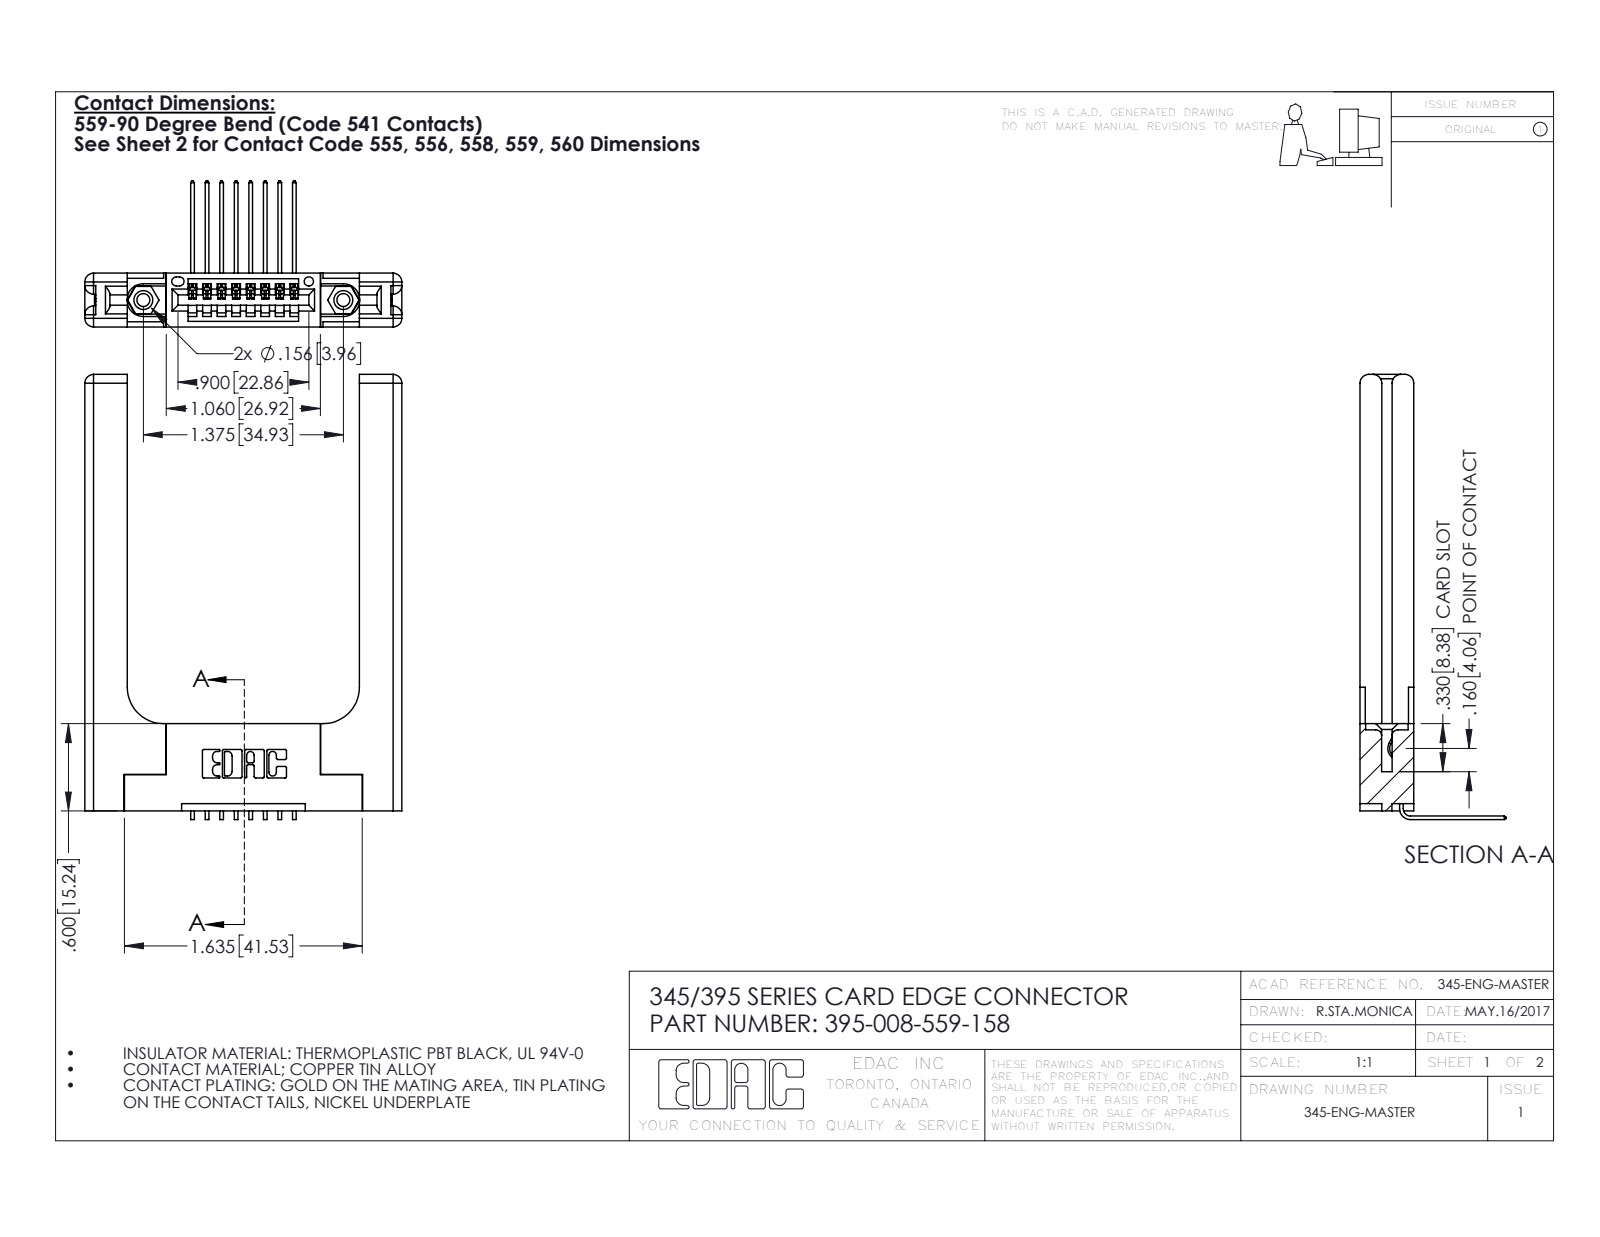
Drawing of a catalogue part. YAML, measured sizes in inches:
part_name: "345 Part_Flush Mounting Lugs - 0.156 Dia-TH; 345-292-001_558 559 Tail - 1; 345-220-058_345-220-058; 345-250-001_345-250-001-102 (+1 more)"
step_written_by: "SolidWorks 2016 (CONFIG_CONTROL_DESIGN)"
units: inches
bodies: {solids: 13, faces: 862, planar: 564, cylindrical: 238, other: 60}
overall_size: [3.059, 2.179, 1.005]
volume: 0.824
surface_area: 18.06
round_holes:
  - {diameter: 0.089, count: 2}
  - {diameter: 0.125, count: 2}
  - {diameter: 0.156, count: 2}
  - {diameter: 0.064, count: 1}
round_bosses_or_shafts:
  - {diameter: 0.155, count: 2}
partial_cylinders:
  - {radius: 0.01, count: 22}
  - {radius: 0.006, count: 16}
  - {radius: 0.06, count: 16}
  - {radius: 0.007, count: 6}
  - {radius: 0.031, count: 6}
  - {radius: 0.026, count: 3}
  - {radius: 0.03, count: 2}
  - {radius: 0.031, count: 2}
face_to_face_distances: [0.37, 0.15, 0.22, 0.072, 0.077, 0.148, 0.298, 1.596, 0.071, 0.2]
hole_center_spacings: [0.27, 1.144, 1.375]
